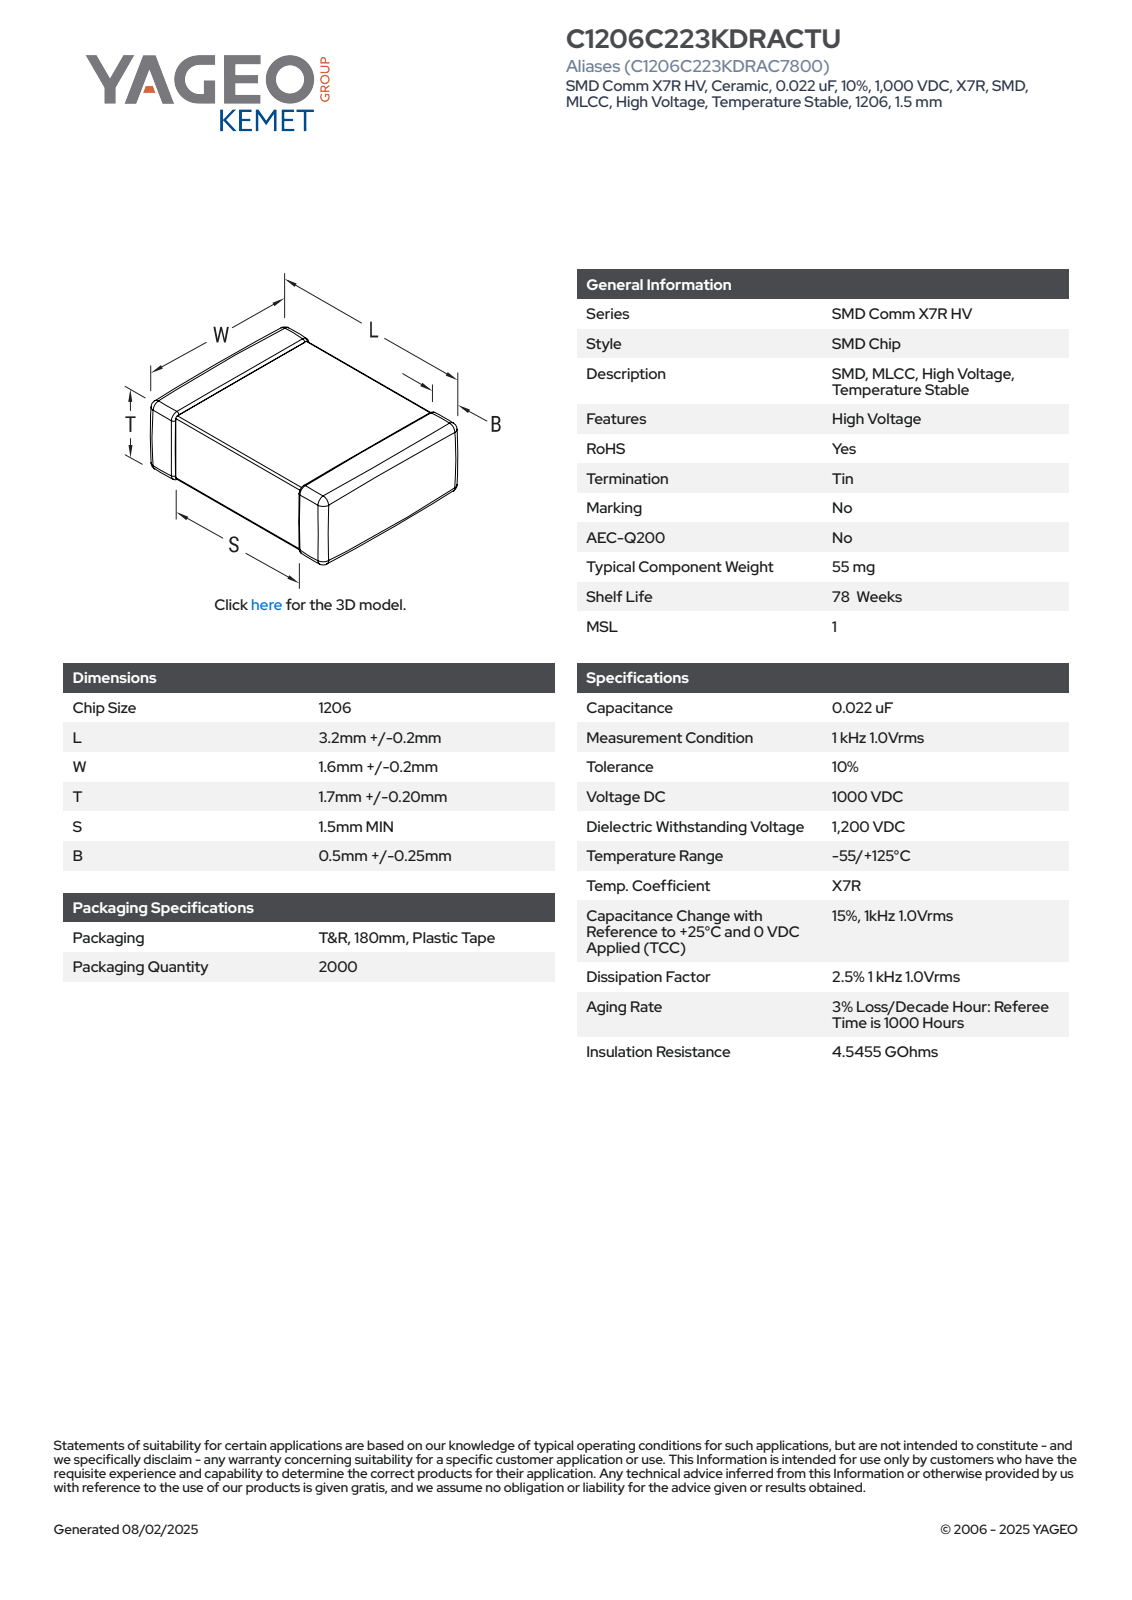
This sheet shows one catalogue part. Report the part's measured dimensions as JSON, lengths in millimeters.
{"part_name": "CCS_CCSTD_1206_L3.4W1.8T1.9B0.5", "step_written_by": "SolidWorks 2021 (AUTOMOTIVE_DESIGN)", "units": "millimeters", "bodies": {"solids": 4, "faces": 125, "planar": 71, "cylindrical": 38, "other": 16}, "overall_size": [3.4, 1.9, 1.8], "volume_mm3": 11, "surface_area_mm2": 32, "face_to_face_distances": [1.76, 1.86, 1.72, 3.4, 1.82, 1.8, 1.9, 1.83, 1.87, 1.57]}
